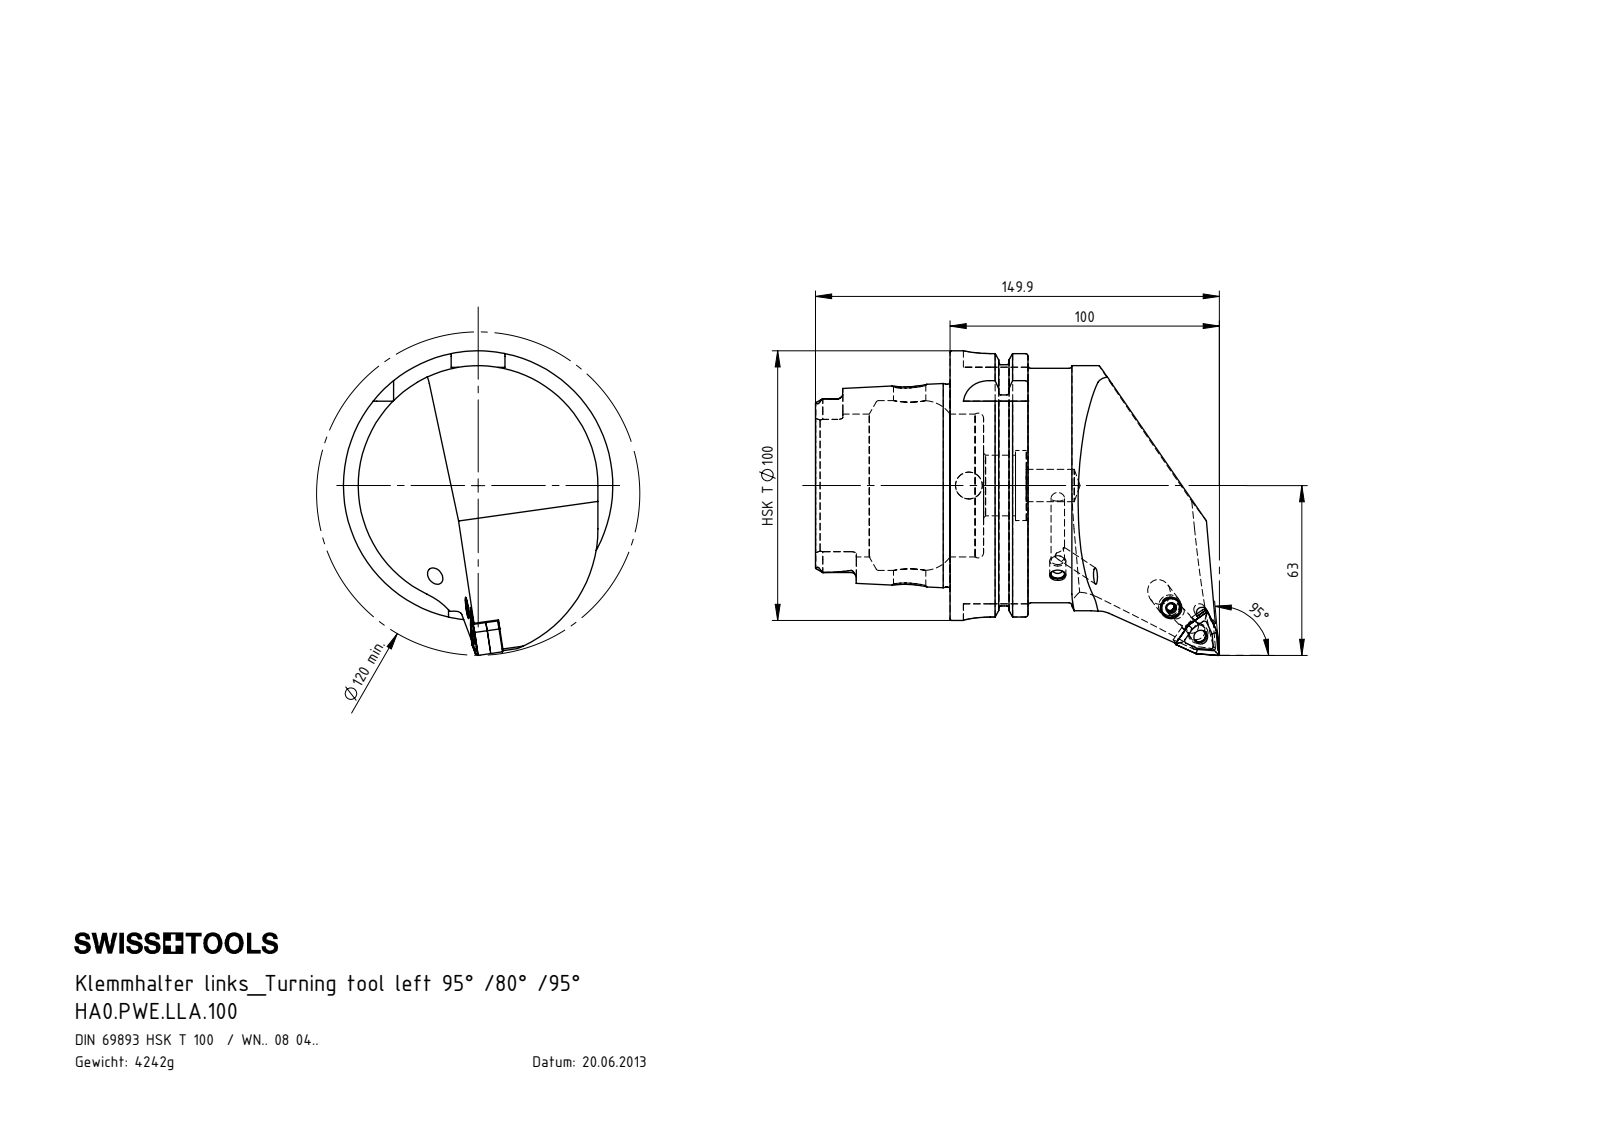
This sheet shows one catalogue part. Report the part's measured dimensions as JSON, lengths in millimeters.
{"part_name": "HA0-PWE.LLA.100; KVT_MB_600_060; WCD-ER1.101.000; WCD-ER4.101.017_A (+4 more)", "step_written_by": "SolidWorks 2012 (AUTOMOTIVE_DESIGN)", "units": "millimeters", "bodies": {"solids": 8, "faces": 398, "planar": 127, "cylindrical": 108, "other": 163}, "overall_size": [149.9, 113, 100], "volume_mm3": 539857, "surface_area_mm2": 70868, "round_holes": [[5, 2], [12, 2], [5.16, 1], [6.7, 1], [7, 1], [7.8, 1], [8.4, 1], [10, 1], [22.5, 1], [26, 1], [53, 1], [63, 1]], "round_bosses_or_shafts": [[100, 1], [91.95, 1], [87, 1], [75.26, 1], [8, 1], [7.9, 1], [6.4, 1], [6, 1]], "partial_cylinders_radius": [[1.9, 6], [2.5, 4], [4.88, 4], [10, 4], [0.4, 3], [1, 3], [3.2, 2], [2.1, 1]], "face_to_face_distances": [12.45, 28.95, 16.5, 49.9, 62.35, 78.85, 87.8, 78.2, 28.3, 15.85], "hole_center_spacings": [15.61]}
